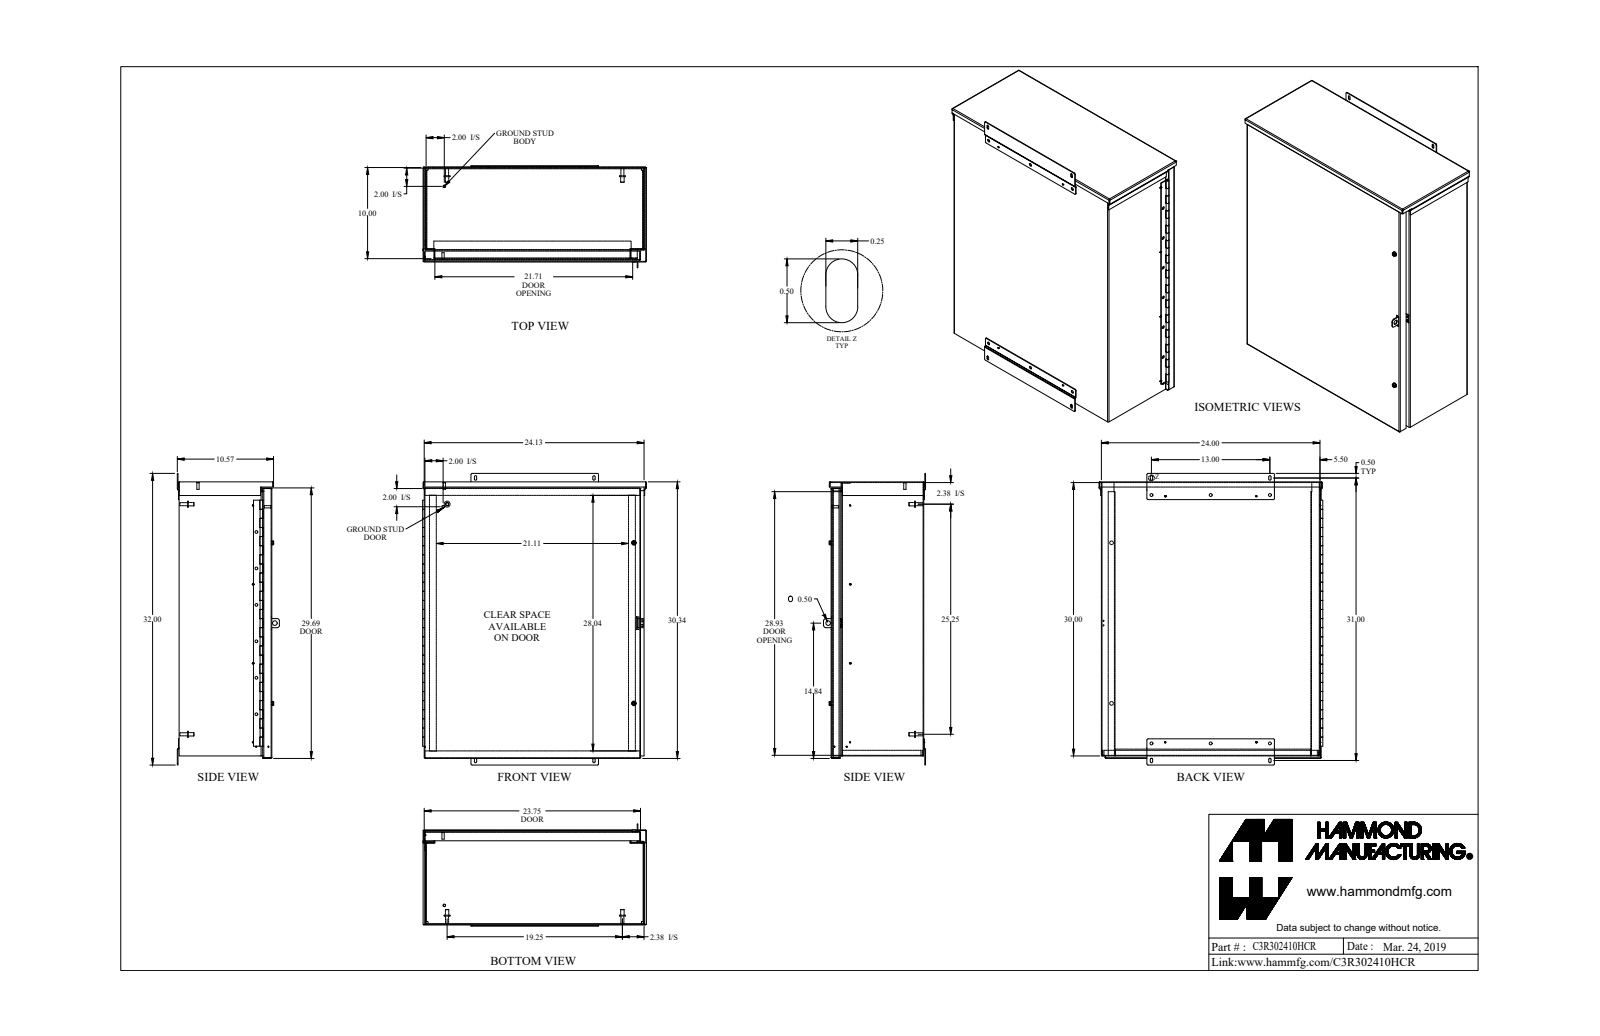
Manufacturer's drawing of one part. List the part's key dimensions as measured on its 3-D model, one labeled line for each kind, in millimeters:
Part name (STEP PRODUCT): C3R302410HCR_Default
STEP written by: SolidWorks 2019 (CONFIG_CONTROL_DESIGN)
Units: millimetres
Bodies: 33 solids, 942 faces (517 planar, 371 cylindrical, 54 other)
Overall size (bounding box): 812.8 × 624.1 × 284.4
Volume: 3 764 000 mm³ · Surface area: 4 017 000 mm²
Round holes (diameter × count): ⌀8 ×9, ⌀7.7 ×6, ⌀3.5 ×4, ⌀3.6 ×4, ⌀6.6 ×3, ⌀6.8 ×2, ⌀7.1 ×2, ⌀7.4 ×2, ⌀10.1 ×2, ⌀4.8 ×1, ⌀12.7 ×1
Round bosses / shafts (diameter × count): ⌀3.3 ×10, ⌀16.5 ×4, ⌀9.5 ×4, ⌀8.4 ×4, ⌀13 ×3, ⌀6.2 ×3, ⌀4.7 ×3, ⌀12.7 ×2
Partial cylindrical surfaces — rounded edges, fillets, slot ends (radius × count): R0.9 ×31, R2.7 ×31, R3.2 ×19, R4.3 ×3, R6.4 ×2
Main face-to-face distances: 1.8, 256.5, 254.7, 258.4, 607.8, 762, 609.6, 605.9, 760.2, 763.8
Hole centre spacings: 101.6, 38.2, 127.1, 165.1, 203.2, 292.1, 700.6, 304.8
